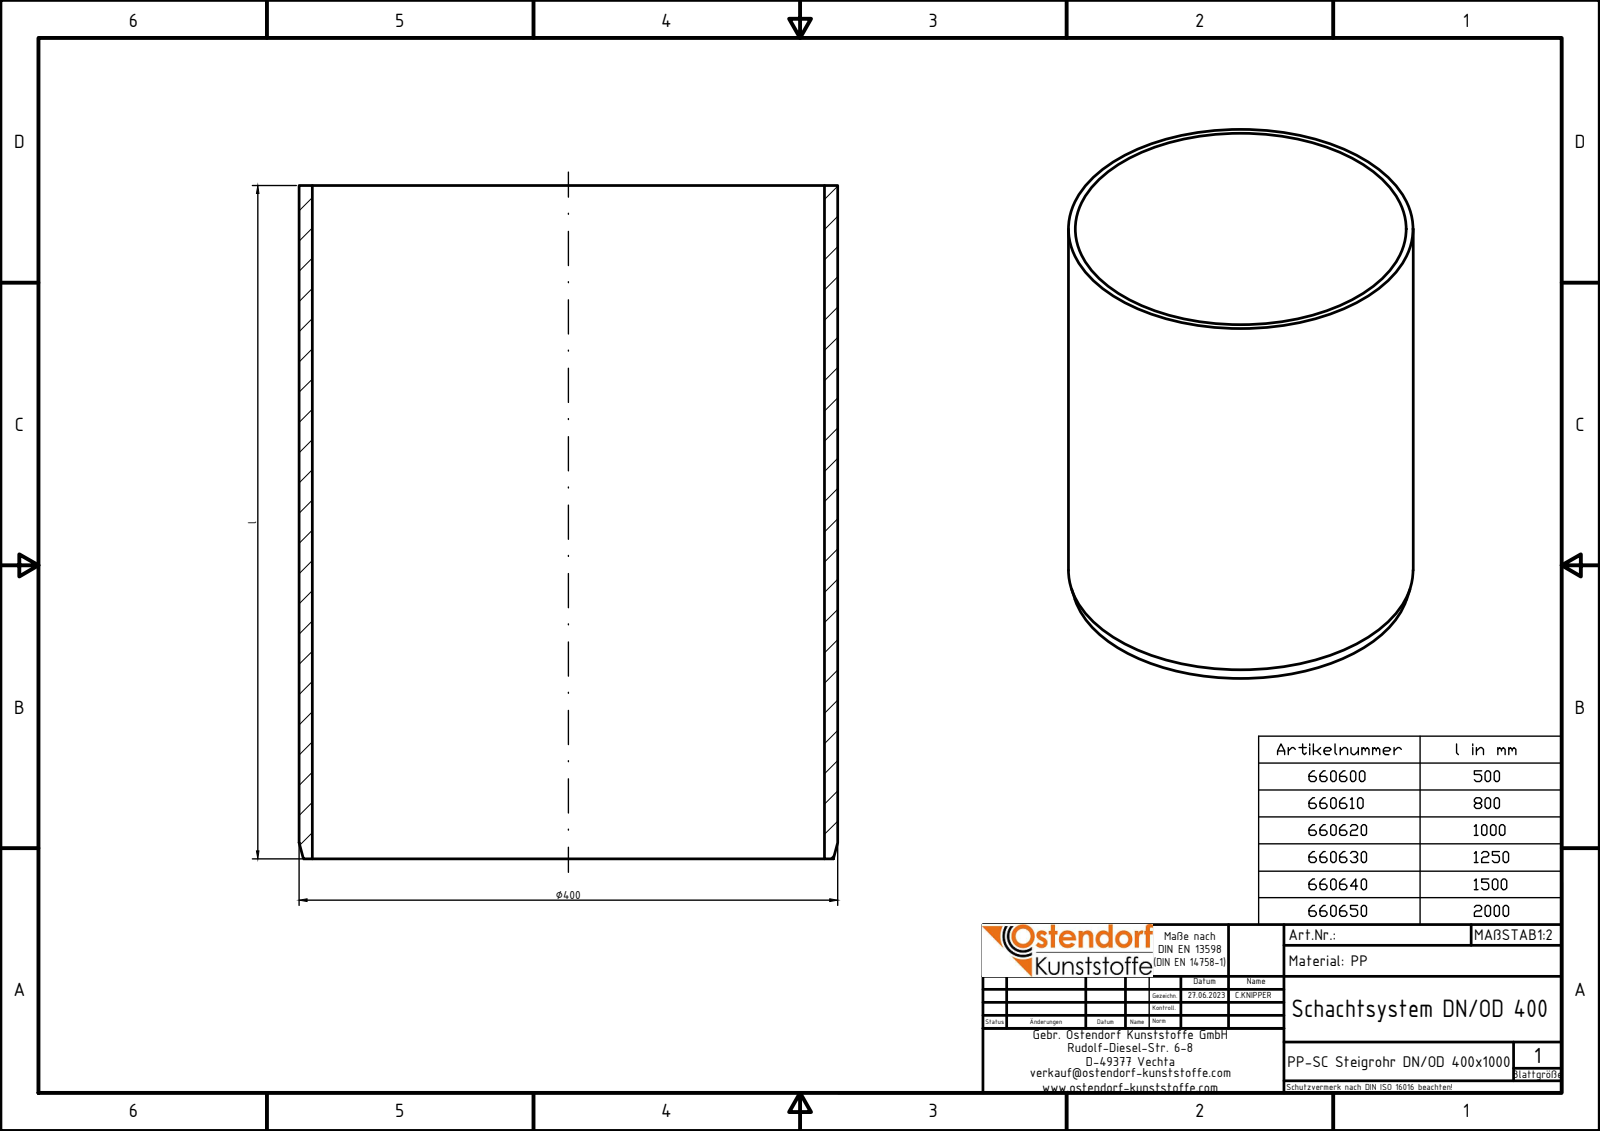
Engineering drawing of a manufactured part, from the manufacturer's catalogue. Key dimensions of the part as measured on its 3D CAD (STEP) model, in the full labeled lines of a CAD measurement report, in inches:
Part name (STEP PRODUCT): 660620
STEP written by: Autodesk Inventor 2020 (AUTOMOTIVE_DESIGN)
Units: inches
Bodies: 1 solid, 5 faces (2 planar, 2 cylindrical, 1 other)
Overall size (bounding box): 39.37 × 15.748 × 15.748
Volume: 731.7 in³ · Surface area: 3 832 in²
Round holes (diameter × count): ⌀14.976 ×1
Round bosses / shafts (diameter × count): ⌀15.748 ×1
Main face-to-face distances: 39.37
